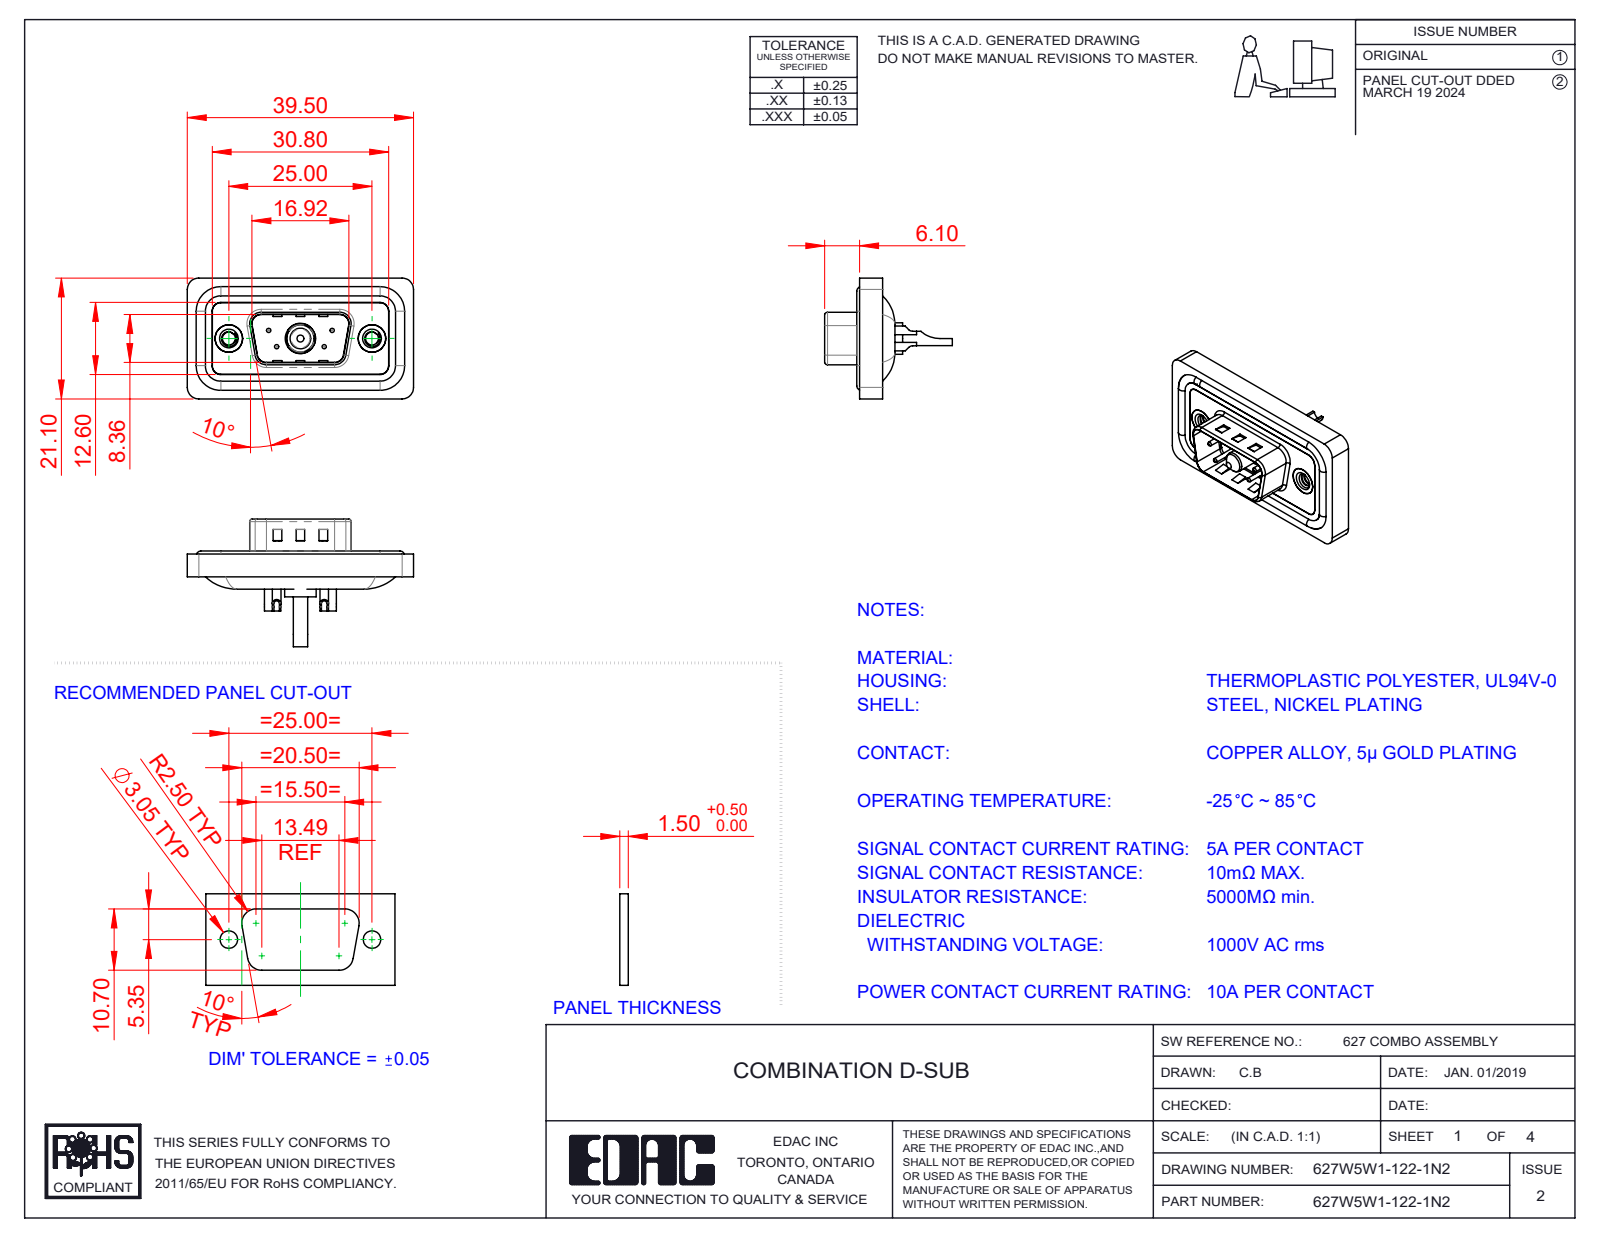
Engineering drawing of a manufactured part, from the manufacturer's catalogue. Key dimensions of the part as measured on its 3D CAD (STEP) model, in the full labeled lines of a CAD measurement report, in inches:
Part name (STEP PRODUCT): 627Combo Shell Front_09 Contacts; 627Combo Shell Rear_09 Contacts; 627Combo Waterproof Housing_09 Contacts; 627Combo Contact Row 2_22 (+5 more)
STEP written by: SolidWorks 2023 (CONFIG_CONTROL_DESIGN)
Units: inches
Bodies: 13 solids, 603 faces (193 planar, 266 cylindrical, 144 other)
Overall size (bounding box): 1.555 × 0.878 × 0.831
Volume: 0.268 in³ · Surface area: 10.88 in²
Round holes (diameter × count): ⌀0.03 ×4, ⌀0.039 ×4, ⌀0.063 ×4, ⌀0.079 ×4, ⌀0.089 ×2, ⌀0.157 ×2, ⌀0.189 ×2, ⌀0.197 ×2, ⌀0.067 ×1, ⌀0.191 ×1, ⌀0.209 ×1
Round bosses / shafts (diameter × count): ⌀0.063 ×4, ⌀0.059 ×4, ⌀0.193 ×2, ⌀0.217 ×1, ⌀0.205 ×1, ⌀0.187 ×1, ⌀0.148 ×1, ⌀0.142 ×1
Partial cylindrical surfaces — rounded edges, fillets, slot ends (radius × count): R0.059 ×22, R0.079 ×18, R0.02 ×8, R0.063 ×8, R0.039 ×6, R0.01 ×4, R0.024 ×4, R0.026 ×4
Main face-to-face distances: 0.016, 0.043, 0.114, 0.063, 0.059, 0.122, 0.02, 0.098, 0.157, 0.031
Hole centre spacings: 0.124, 0.225, 0.28, 0.492, 0.713, 0.173, 0.173, 0.327
